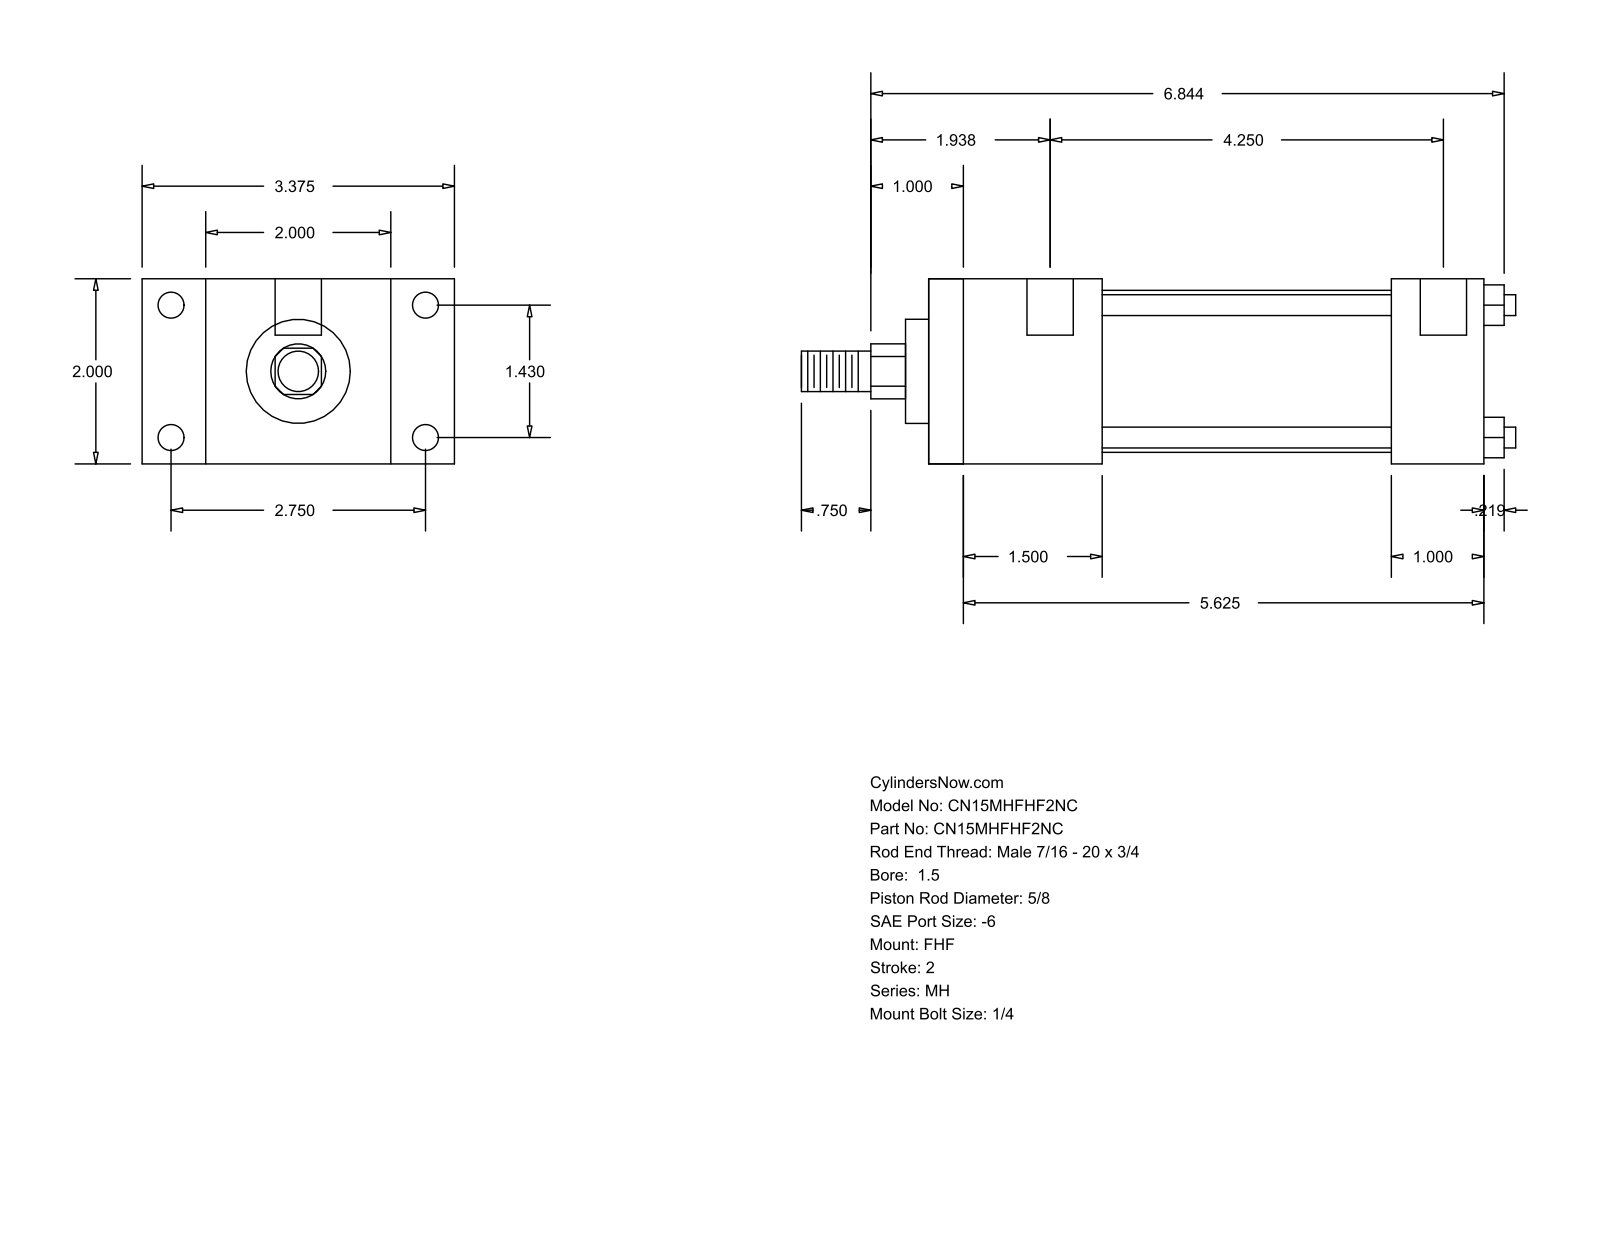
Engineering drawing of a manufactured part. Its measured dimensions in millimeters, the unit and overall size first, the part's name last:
Units: millimetres
Overall size (bounding box): 196.06 × 85.72 × 50.8
Round holes (diameter × count): ⌀5.56 ×4, ⌀7.14 ×4, ⌀12.7 ×2
Round bosses / shafts (diameter × count): ⌀5.71 ×4, ⌀44.45 ×1, ⌀28.57 ×1, ⌀15.88 ×1, ⌀11.11 ×1
Partial cylindrical surfaces — rounded edges, fillets, slot ends (radius × count): R7.54 ×1
Main face-to-face distances: 50.8, 17.46, 68.26, 47.62, 85.72, 152.4, 104.78, 25.4, 127, 79.38
Hole centre spacings: 36.32, 69.84, 78.72, 111.12, 3.17, 107.95
Bodies: 0 solids, 88 faces (60 planar, 28 cylindrical, 0 other)
Part name (STEP PRODUCT): MH_FHF__0150_0.625
STEP written by: GSSL Pune (CONFIG_CONTROL_DESIGN)
